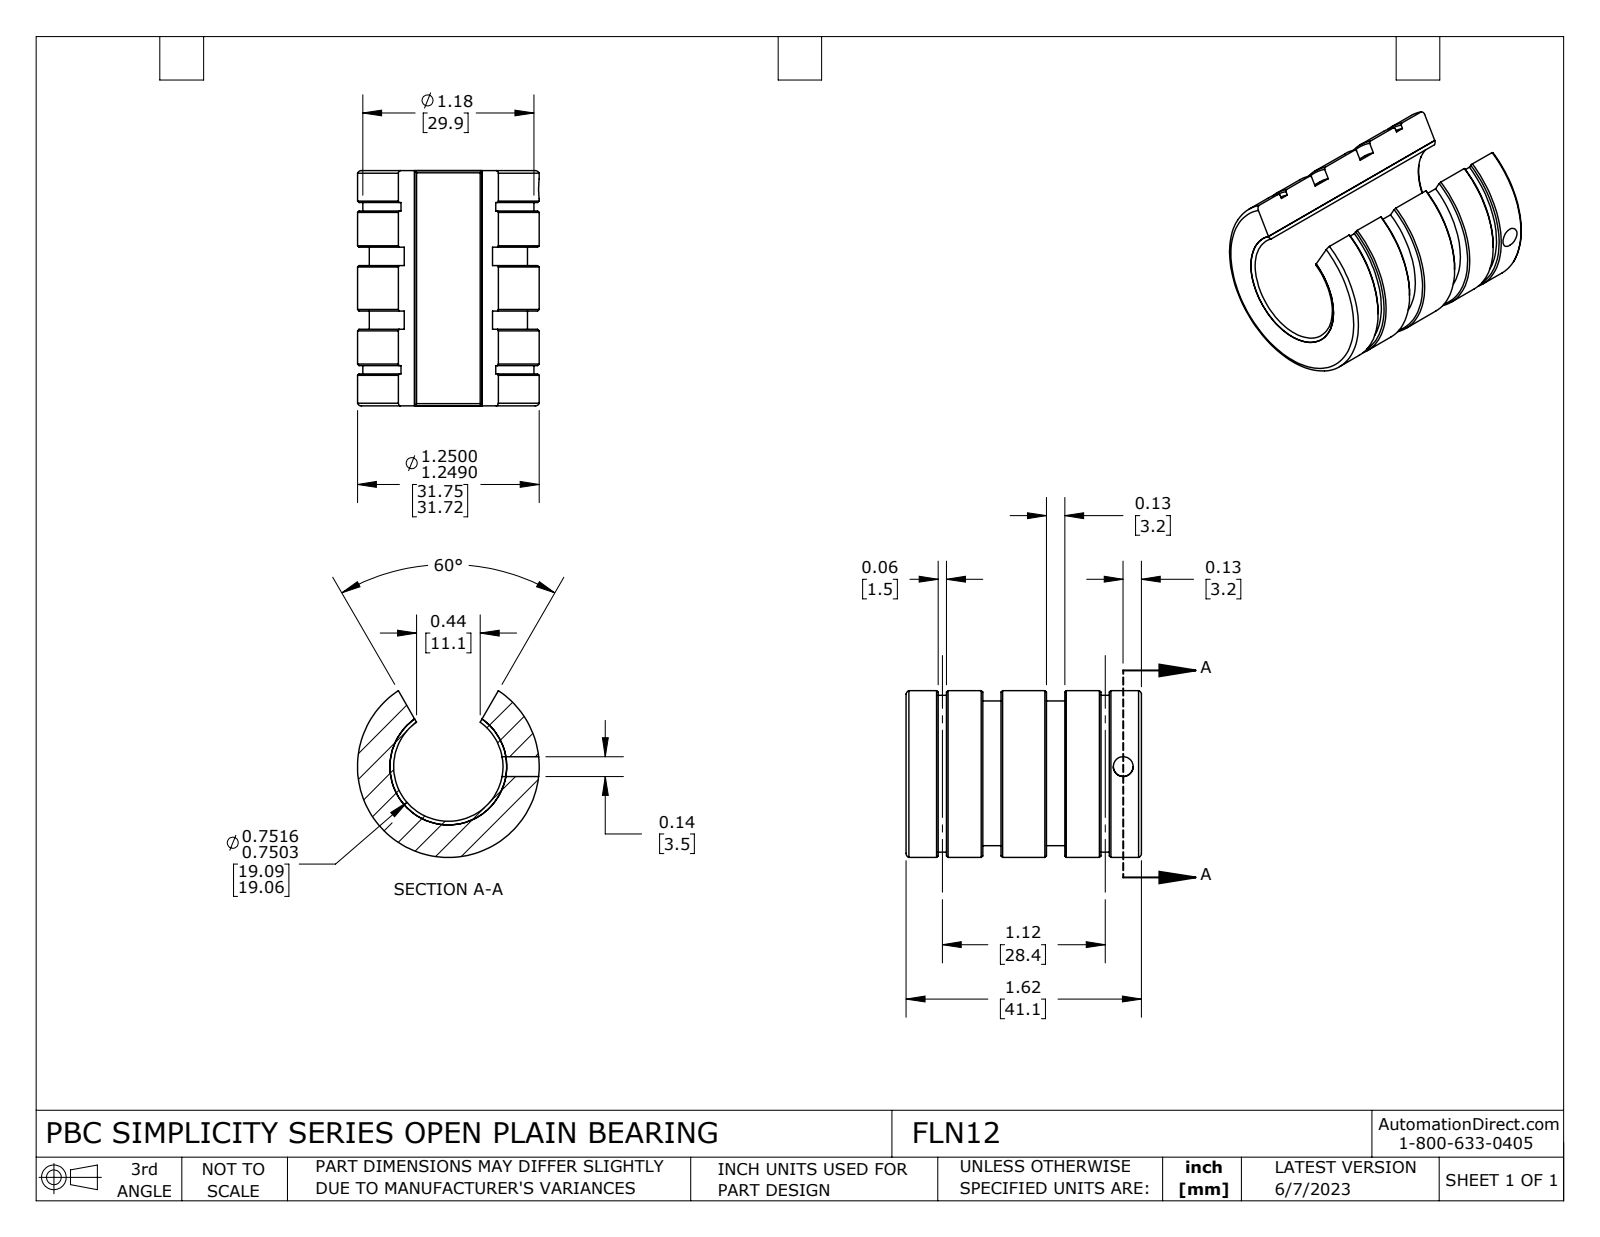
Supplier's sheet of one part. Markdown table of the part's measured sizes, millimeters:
| quantity | value |
| --- | --- |
| part name | FLN12 |
| STEP written by | SolidWorks 2021 (CONFIG_CONTROL_DESIGN) |
| units | millimeters |
| bodies | 2 solids, 82 faces (14 planar, 40 cylindrical, 28 other) |
| overall size | 41.1 × 31.7 × 29.1 |
| volume | 15 500 mm³ |
| surface area | 11 540 mm² |
| round holes (diameter × count) | 3.5 × 1, 19.1 × 1, 20.4 × 1 |
| round bosses / shafts (diameter × count) | 31.7 × 1, 29.9 × 1, 27.6 × 1 |
| main face-to-face distances | 41.1, 13.4, 27.7, 16.6, 24.5, 3.2, 11.1, 7.9, 14.3, 5.6 |
